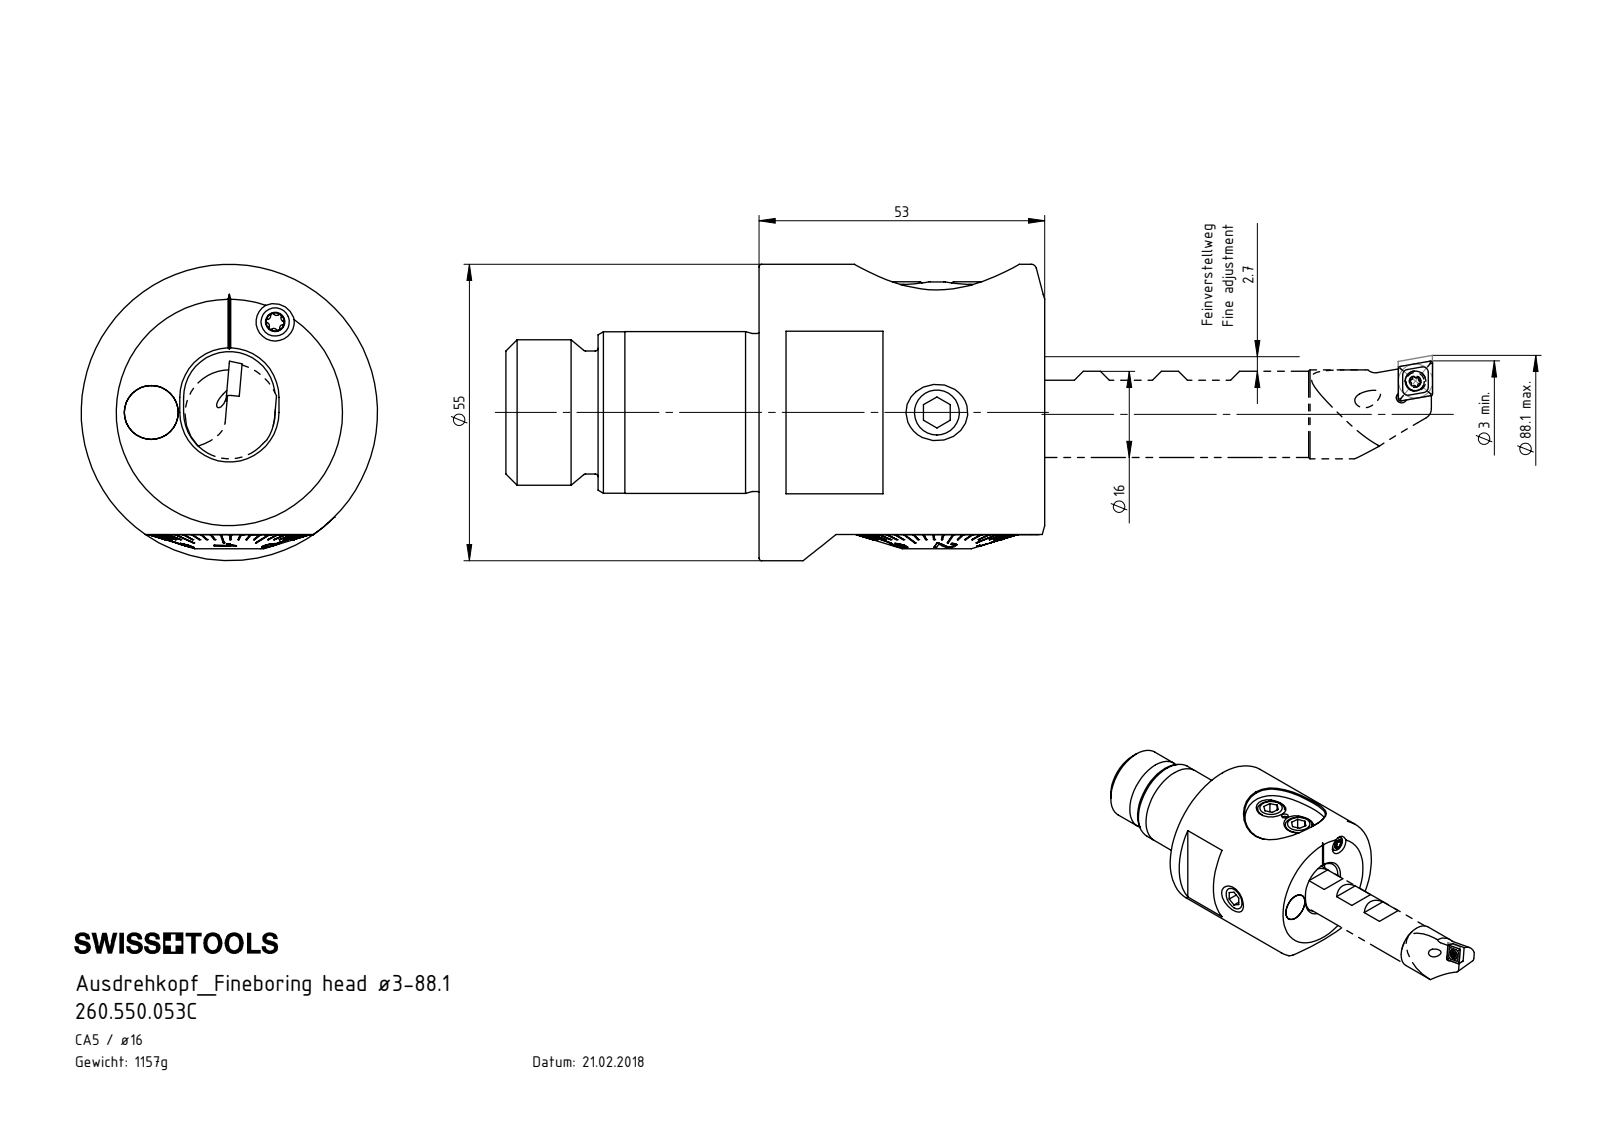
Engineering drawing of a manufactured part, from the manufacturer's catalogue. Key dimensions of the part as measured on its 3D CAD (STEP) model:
Part name (STEP PRODUCT): A55-BG3.011.033_A_gekrzt; A55-BG1.014.041; WCB-ER2.001.009_A; A55-BG1.011.041_E (+8 more)
STEP written by: SolidWorks 2017 (CONFIG_CONTROL_DESIGN)
Units: millimetres
Bodies: 16 solids, 739 faces (323 planar, 132 cylindrical, 284 other)
Overall size (bounding box): 100 × 55 × 55
Volume: 131 487 mm³ · Surface area: 42 156 mm²
Round holes (diameter × count): ⌀8.5 ×4, ⌀1 ×1, ⌀1.6 ×1, ⌀2 ×1, ⌀3.3 ×1, ⌀4.2 ×1, ⌀8 ×1, ⌀10 ×1, ⌀11.75 ×1, ⌀12.4 ×1, ⌀14 ×1, ⌀14.2 ×1
Round bosses / shafts (diameter × count): ⌀10 ×3, ⌀30 ×2, ⌀55 ×1, ⌀29.98 ×1, ⌀29.95 ×1, ⌀29.9 ×1, ⌀29.3 ×1, ⌀27 ×1
Partial cylindrical surfaces — rounded edges, fillets, slot ends (radius × count): R0.34 ×6, R0.59 ×6, R3.2 ×3, R8.5 ×2, R0.5 ×1, R3.5 ×1, R27.5 ×1, R27.51 ×1
Main face-to-face distances: 53, 46, 3.68, 50, 5.3, 6.48, 1.18, 2.8, 2.5, 5
Hole centre spacings: 14.5, 7.25, 0.37, 14.7, 15.07, 18.83, 19.16, 20.91
